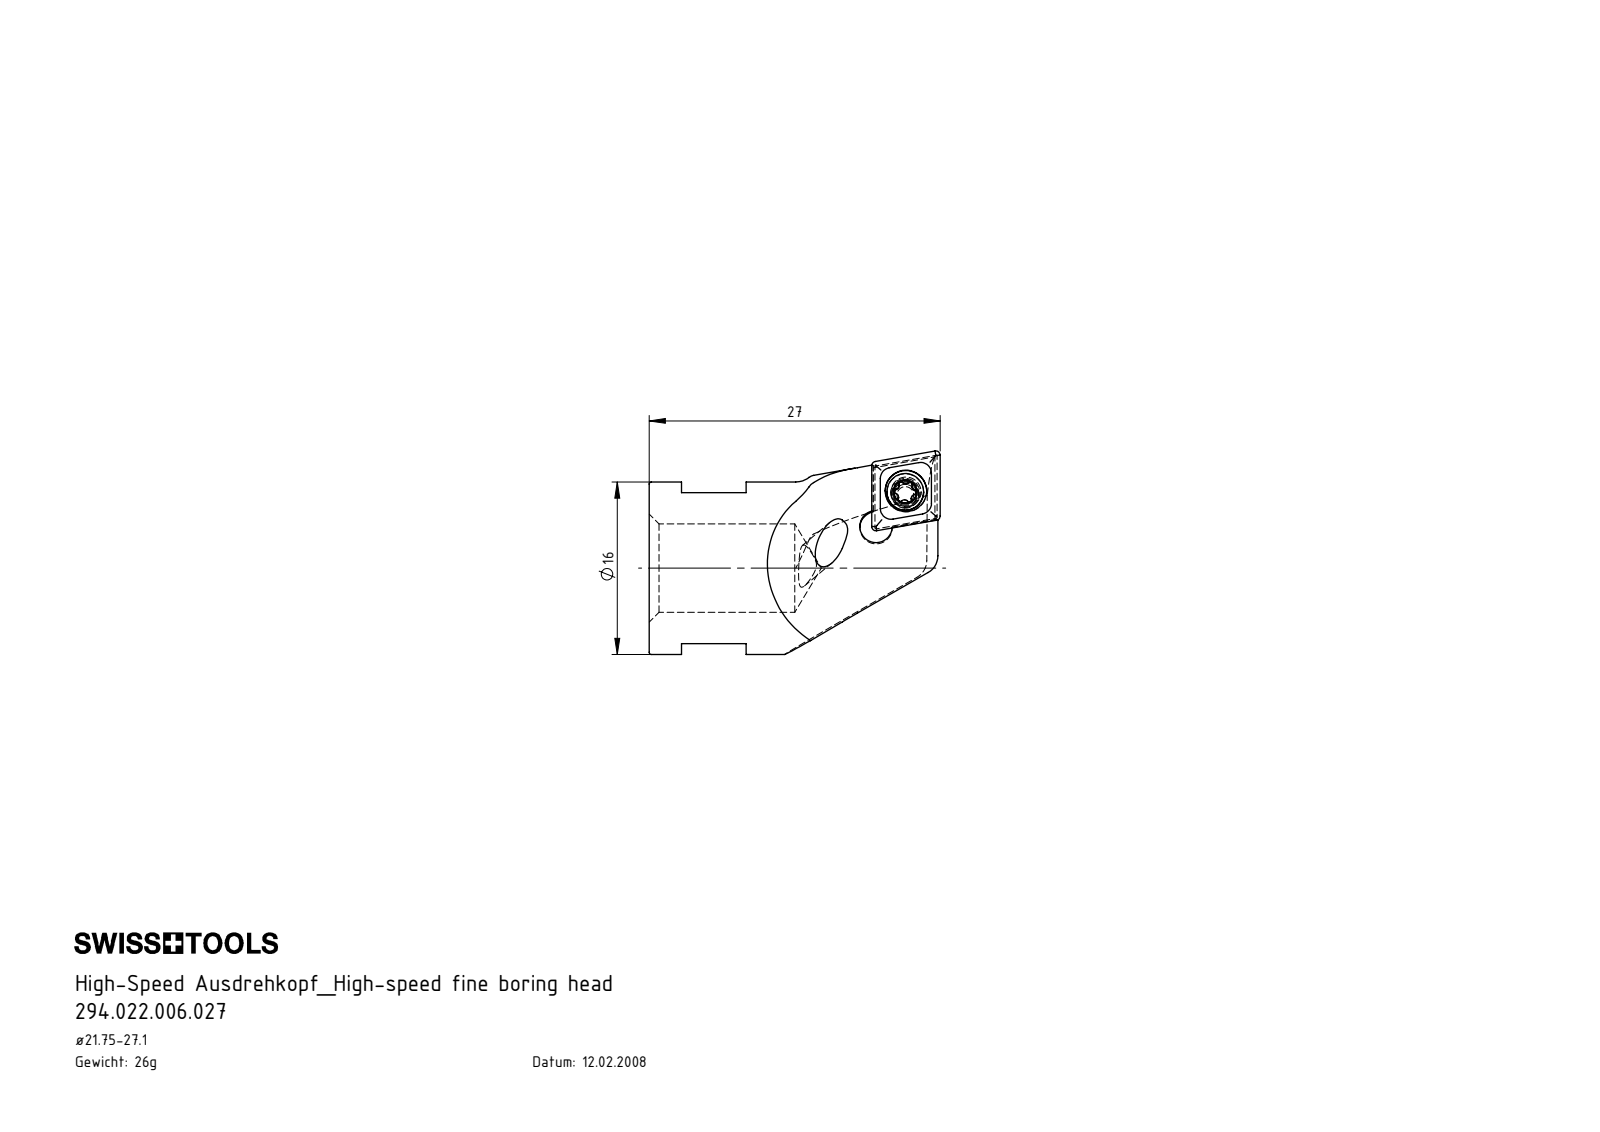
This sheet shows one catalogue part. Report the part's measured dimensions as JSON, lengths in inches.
{"part_name": "WCA-ER2.001.006_A; HS0-A22.K11.027_B; CCMT060204; HS0.A22.K11.027", "step_written_by": "SolidWorks 2017 (AUTOMOTIVE_DESIGN)", "units": "inches", "bodies": {"solids": 3, "faces": 121, "planar": 34, "cylindrical": 35, "other": 52}, "overall_size": [1.063, 0.743, 0.63], "volume_in3": 0.198, "surface_area_in2": 3.311, "round_holes": [[0.081, 1], [0.11, 1], [0.118, 1], [0.152, 1], [0.323, 1]], "round_bosses_or_shafts": [[0.63, 1], [0.134, 1], [0.098, 1]], "partial_cylinders_radius": [[0.008, 6], [0.014, 5], [0.014, 1], [0.059, 1], [0.071, 1], [0.079, 1]], "face_to_face_distances": [0.09, 0.552, 0.236, 0.094, 0.354, 0.118, 0.819, 0.701, 0.465, 0.058]}
